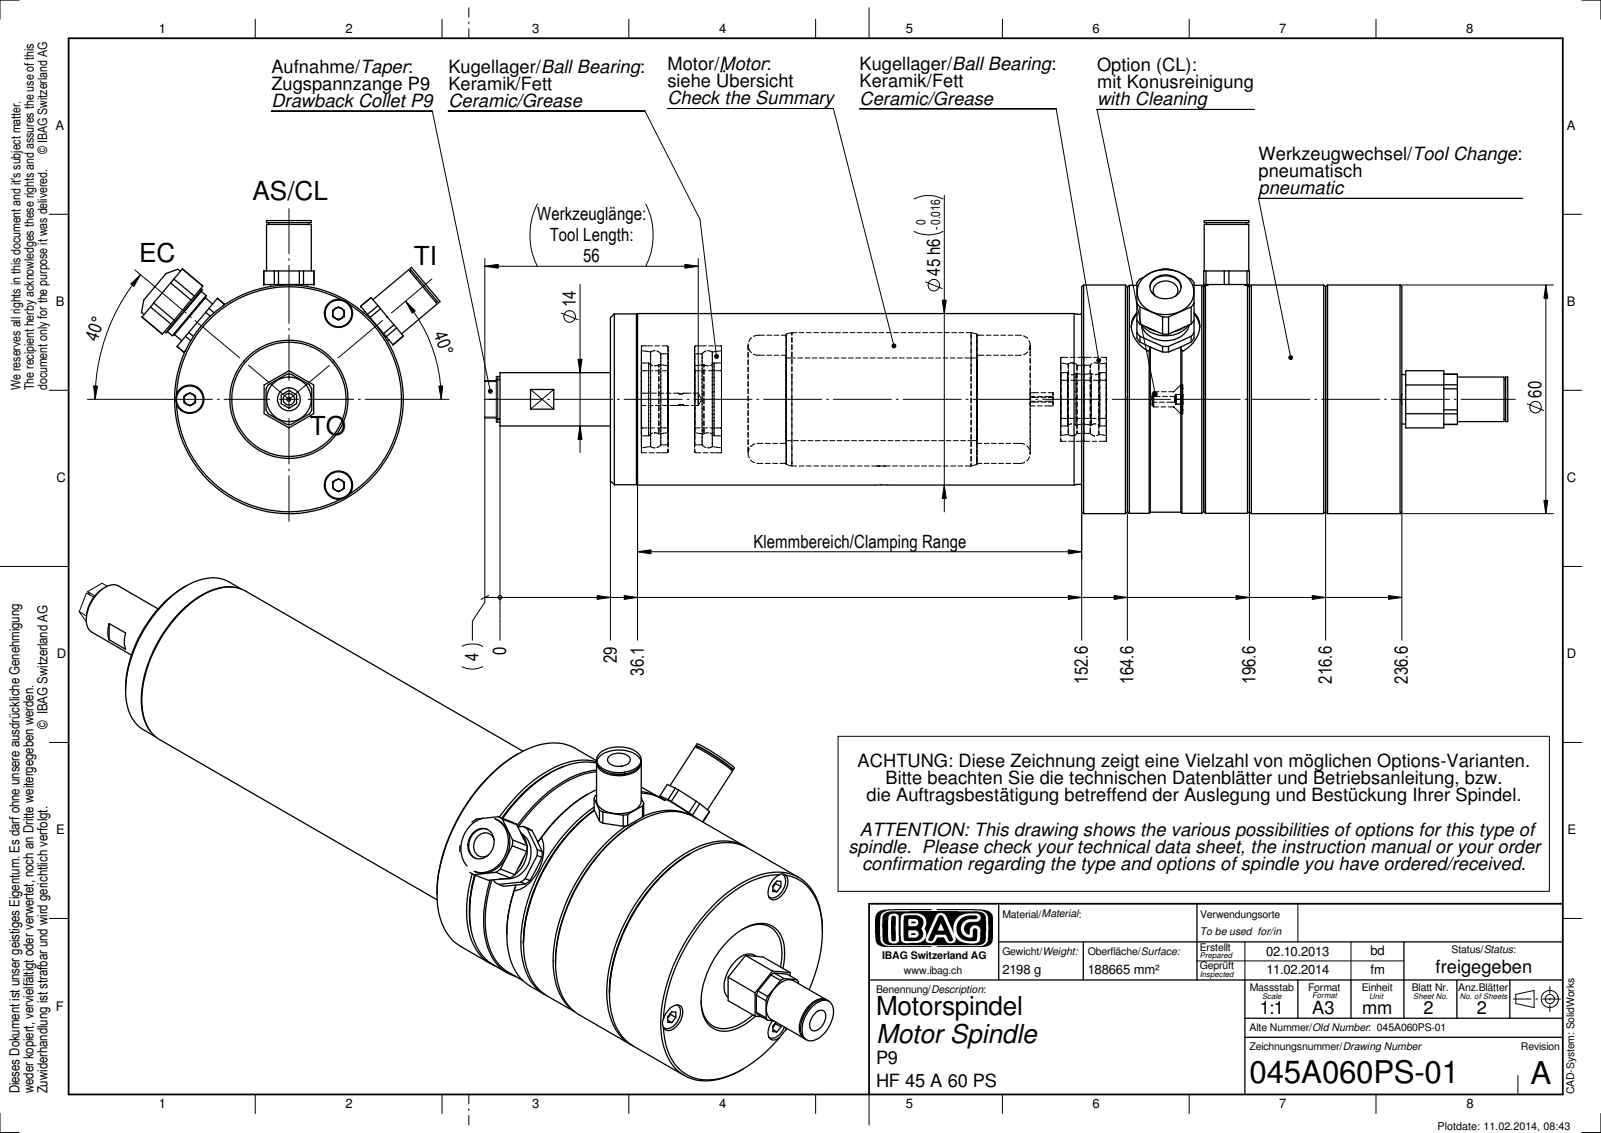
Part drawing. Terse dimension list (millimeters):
name: 045A060PS-01A
written by: SolidWorks 2012 (CONFIG_CONTROL_DESIGN)
unit: mm
bodies: 0 solids, 374 faces (156 planar, 126 cylindrical, 92 other)
size: 268.34 × 78.31 × 76.88
holes: 3× ⌀6, 3× ⌀7.4, 2× ⌀4.2, 1× ⌀3, 1× ⌀3.3, 1× ⌀6.5, 1× ⌀8.2, 1× ⌀14.4
bosses: 4× ⌀5.7, 3× ⌀11.7, 2× ⌀10.53, 1× ⌀60, 1× ⌀59.8, 1× ⌀59.2, 1× ⌀45, 1× ⌀44.8
rounds: 3× R6.6, 2× R8.25, 1× R9
face distances: 20, 32, 52, 12, 72, 135.6, 155.6, 207.6, 167.6, 40
hole spacings: 26, 45.03, 13.46, 36.77, 25.99, 50.22, 50.23, 52
